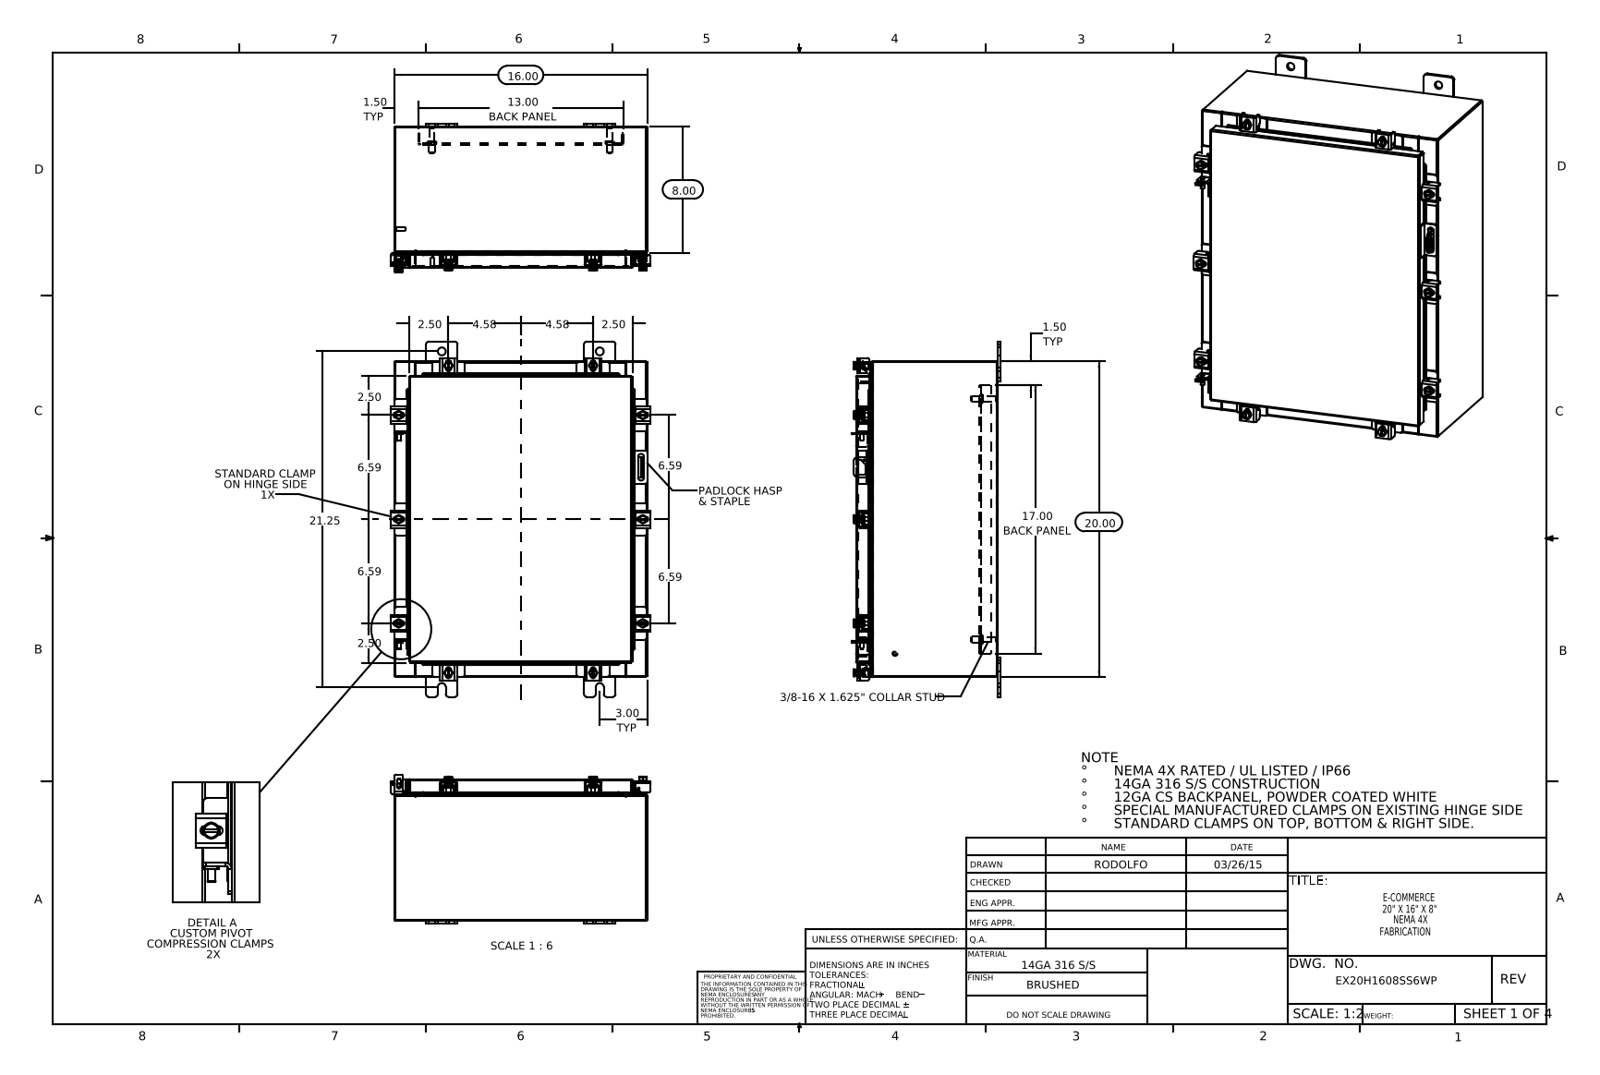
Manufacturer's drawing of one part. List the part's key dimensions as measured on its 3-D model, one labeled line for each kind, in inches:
Part name (STEP PRODUCT): EX20H1608SS6WP Clamp Bracket; N-WMT04X30402202210-00 22101002; EX20H1608SS6WP Clamp Assembly; Clamp Top_RTP31 (+8 more)
STEP written by: SolidWorks 2014 (CONFIG_CONTROL_DESIGN)
Units: inches
Bodies: 71 solids, 1784 faces (955 planar, 685 cylindrical, 144 other)
Overall size (bounding box): 22.5 × 16.421 × 9.453
Volume: 135.4 in³ · Surface area: 3 406 in²
Round holes (diameter × count): ⌀0.213 ×10, ⌀0.26 ×10, ⌀0.5 ×8, ⌀0.125 ×1, ⌀0.25 ×1
Round bosses / shafts (diameter × count): ⌀0.5 ×10, ⌀0.25 ×10, ⌀0.399 ×8, ⌀0.625 ×4, ⌀0.375 ×4, ⌀0.33 ×4, ⌀0.315 ×2, ⌀0.236 ×2
Partial cylindrical surfaces — rounded edges, fillets, slot ends (radius × count): R0.06 ×46, R0.013 ×24, R0.19 ×24, R0.088 ×22, R0.141 ×20, R0.12 ×18, R0.09 ×16, R0.1 ×16
Main face-to-face distances: 0.075, 8.9, 15.925, 8.975, 8.826, 19.925, 0.104, 1, 1.075, 7.826
Hole centre spacings: 2.347, 4.44, 6.594, 10.222, 12.696, 14.374, 15.683, 16.62
